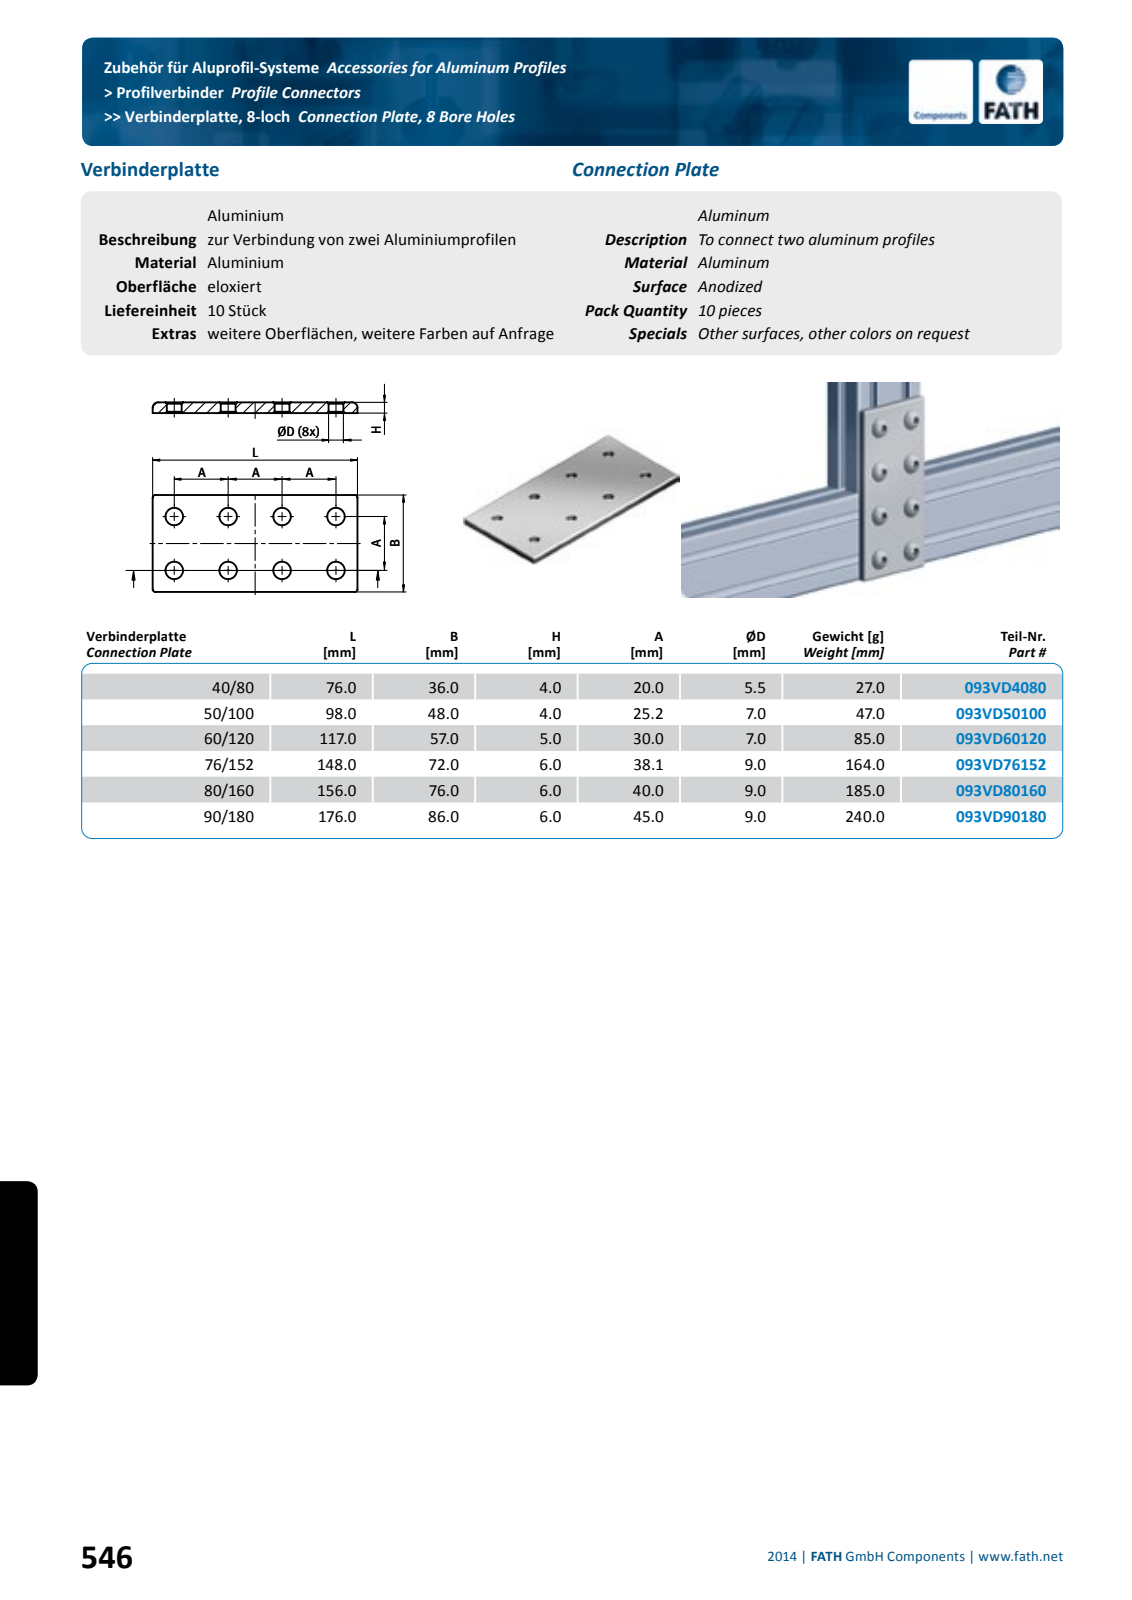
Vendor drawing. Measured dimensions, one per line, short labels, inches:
name: fath_093vd60120
written by: Spatial InterOp 3D (automotive_design)
unit: in
bodies: 1 solid, 66 faces (6 planar, 24 cylindrical, 36 other)
size: 4.606 × 2.244 × 0.197
volume: 1.919 in³; area: 23.13 in²
holes: 8× ⌀0.276
rounds: 8× R0.079
face distances: 0.197, 2.244, 4.606
hole spacings: 1.181, 1.67, 2.362, 2.641, 3.543, 3.735
